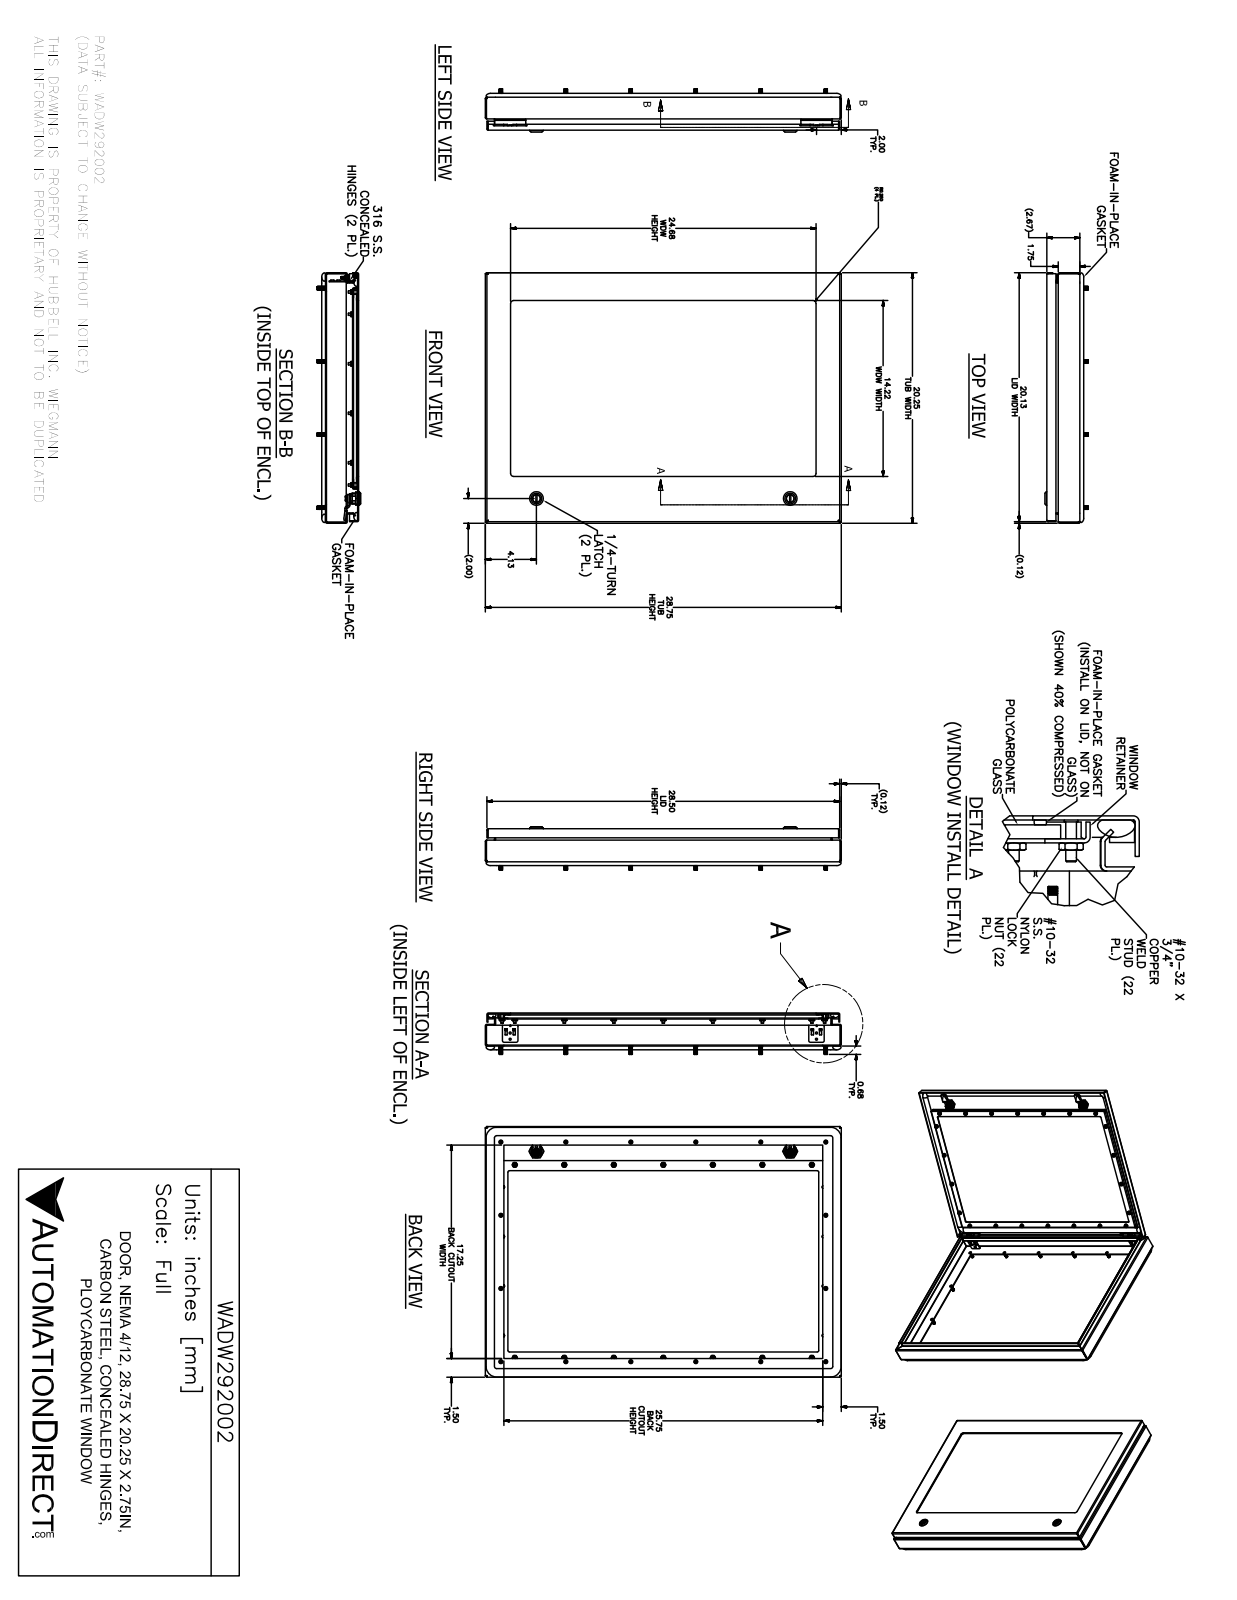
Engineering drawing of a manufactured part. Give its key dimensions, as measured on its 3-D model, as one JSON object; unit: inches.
{"part_name": "WADW292002", "step_written_by": "SolidWorks 2017 (AUTOMOTIVE_DESIGN)", "units": "inches", "bodies": {"solids": 92, "faces": 2697, "planar": 1046, "cylindrical": 816, "other": 835}, "overall_size": [28.75, 20.25, 3.525], "volume_in3": 194.1, "surface_area_in2": 2802, "round_holes": [[0.156, 24], [0.281, 22], [0.249, 9], [0.093, 4], [0.152, 4], [0.167, 4], [0.172, 4], [0.188, 4], [0.197, 2], [0.315, 2], [0.394, 2], [0.402, 2]], "round_bosses_or_shafts": [[0.25, 30], [0.19, 22], [0.313, 8], [0.249, 6], [0.36, 4], [0.32, 4], [0.256, 4], [0.164, 4]], "partial_cylinders_radius": [[0.012, 54], [0.031, 34], [0.05, 26], [0.105, 24], [0.02, 23], [0.125, 20], [0.016, 18], [0.032, 8]], "face_to_face_distances": [0.074, 0.25, 0.337, 0.087, 0.411, 0.161, 2.593, 2.182, 2.432, 2.519], "hole_center_spacings": [4, 8, 16.1, 12, 17.527, 19.678, 15.595, 16]}
